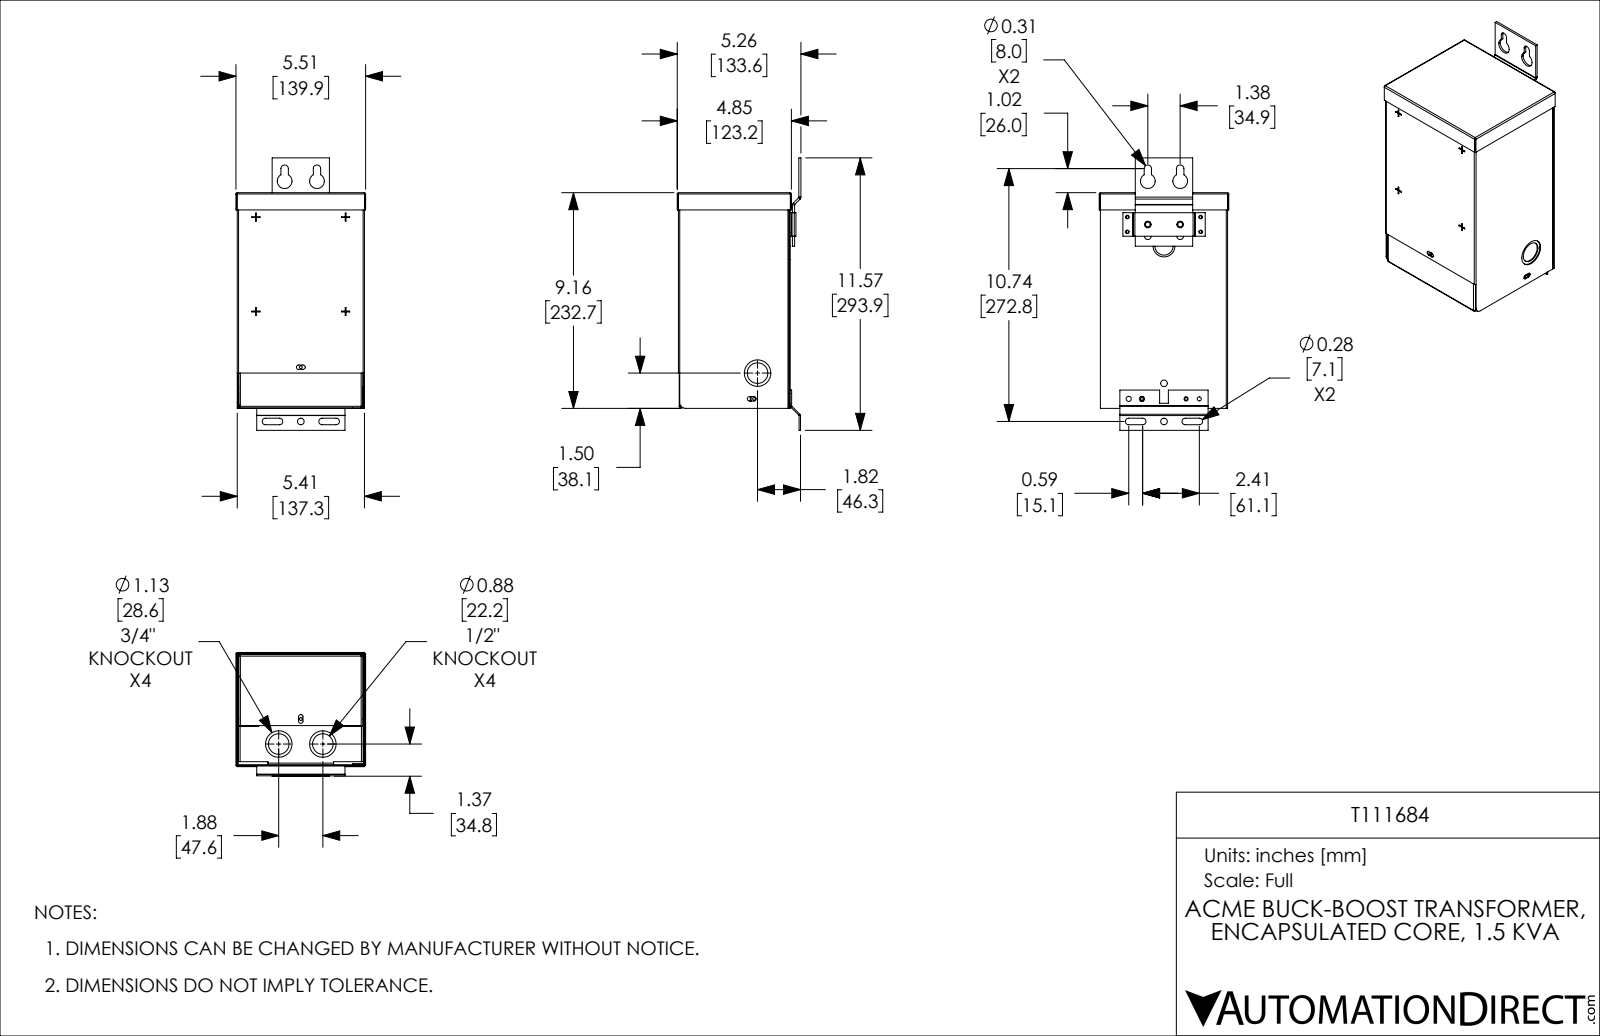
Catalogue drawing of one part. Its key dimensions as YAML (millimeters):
part_name: "T111684"
step_written_by: "SolidWorks 2021 (CONFIG_CONTROL_DESIGN)"
units: millimeters
bodies: {solids: 7, faces: 521, planar: 329, cylindrical: 152, other: 40}
overall_size: [293.87, 139.9, 133.57]
volume: 177414
surface_area: 368059
round_holes:
  - {diameter: 7.14, count: 6}
  - {diameter: 3.05, count: 5}
  - {diameter: 22.22, count: 3}
  - {diameter: 28.57, count: 3}
  - {diameter: 4.37, count: 2}
  - {diameter: 4.76, count: 2}
  - {diameter: 5.11, count: 2}
  - {diameter: 5.56, count: 2}
  - {diameter: 15.88, count: 2}
round_bosses_or_shafts:
  - {diameter: 29.79, count: 1}
  - {diameter: 23.44, count: 1}
partial_cylinders:
  - {radius: 0.51, count: 10}
  - {radius: 2.38, count: 10}
  - {radius: 0.79, count: 8}
  - {radius: 1.42, count: 8}
  - {radius: 1.7, count: 8}
  - {radius: 0.38, count: 4}
  - {radius: 1.9, count: 4}
  - {radius: 3.57, count: 4}
face_to_face_distances: [0.91, 119.74, 136.41, 118.83, 135.5, 137.32, 120.65, 231.14, 1.29, 2.2]
hole_center_spacings: [34.92, 12.7, 14.29, 29.09, 34.08, 35.98, 37.16, 41.6]
